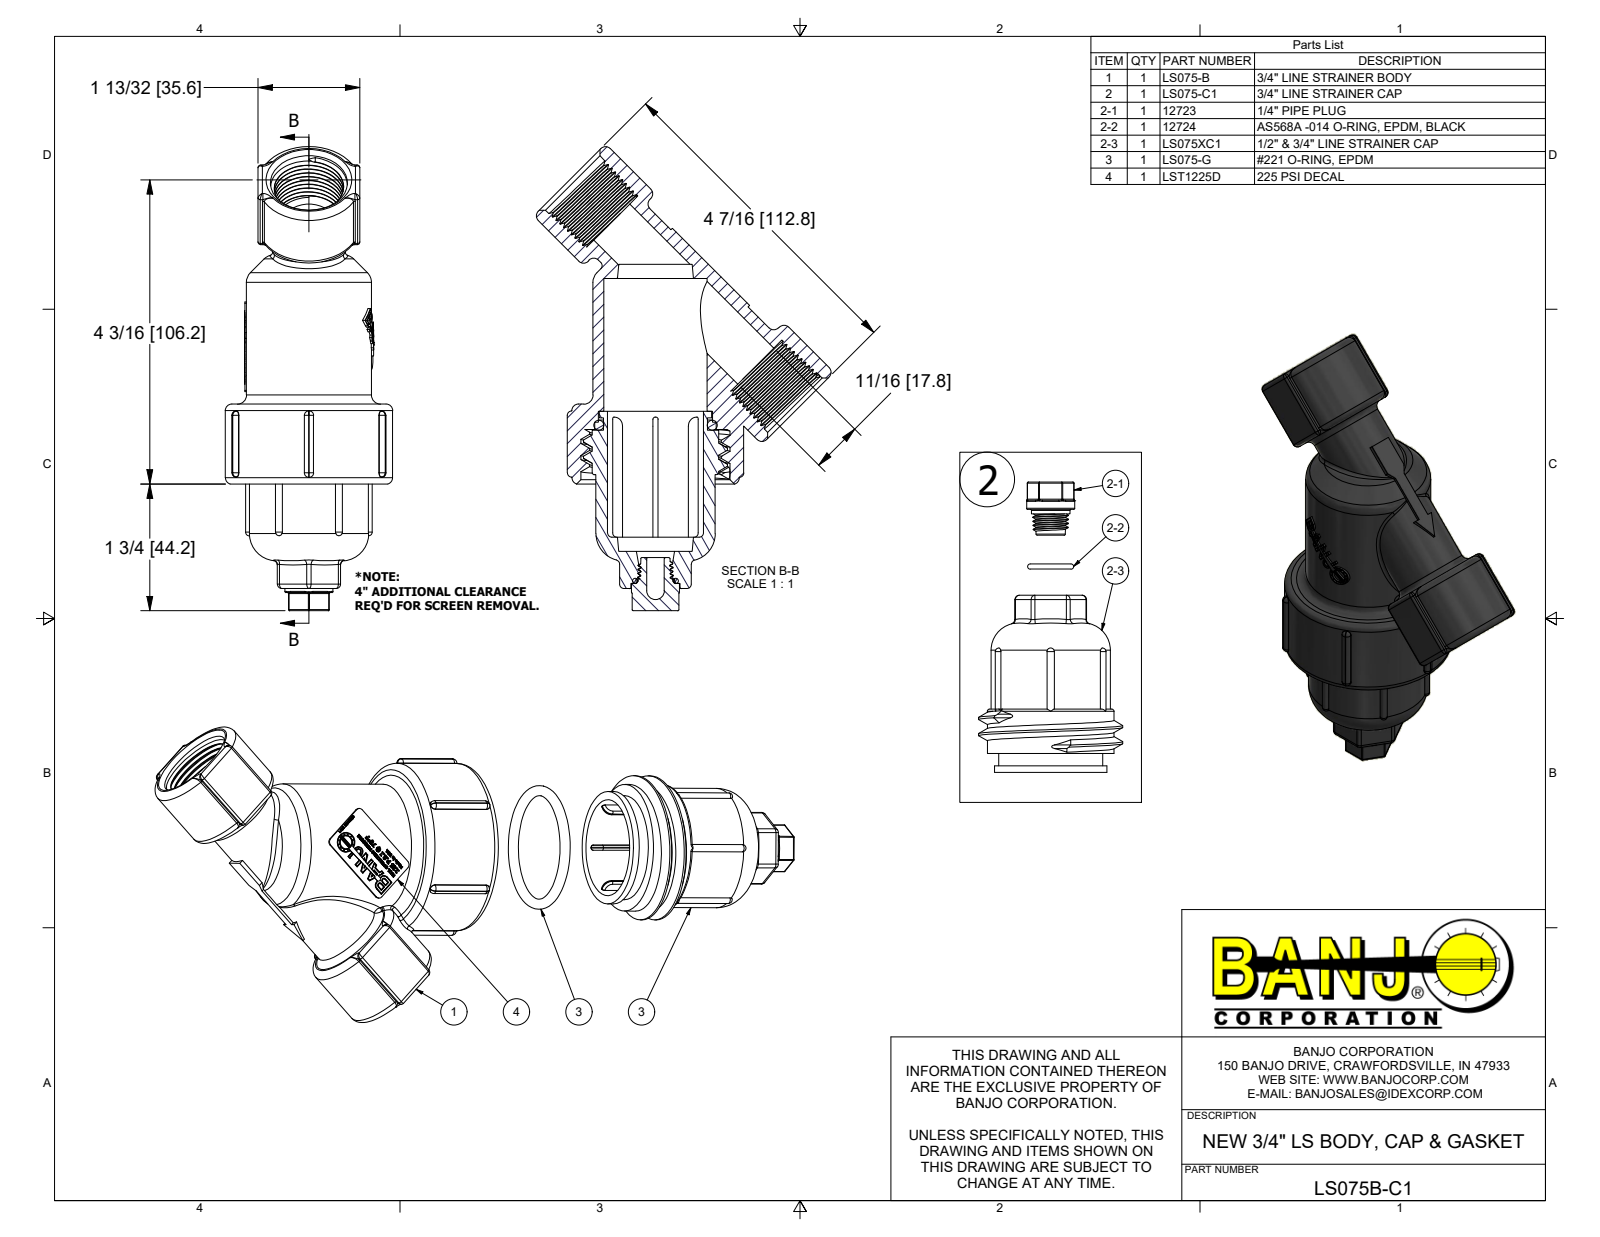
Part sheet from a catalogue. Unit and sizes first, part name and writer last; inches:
Units: inches
Overall size (bounding box): 21.064 × 21.064 × 2.3
Round holes (diameter × count): ⌀0.181 ×2, ⌀0.257 ×2, ⌀0.7 ×2, ⌀0.24 ×1, ⌀0.675 ×1, ⌀1.32 ×1, ⌀1.42 ×1, ⌀1.57 ×1, ⌀1.671 ×1, ⌀1.809 ×1, ⌀2.05 ×1
Round bosses / shafts (diameter × count): ⌀0.27 ×2, ⌀2.3 ×1, ⌀1.981 ×1, ⌀1.74 ×1, ⌀1.72 ×1, ⌀1.64 ×1, ⌀1.545 ×1, ⌀1.43 ×1
Partial cylindrical surfaces — rounded edges, fillets, slot ends (radius × count): R0.06 ×75, R0.03 ×34, R0.015 ×18, R0.125 ×8, R0.05 ×6, R0.026 ×4, R0.033 ×4, R0.063 ×4
Main face-to-face distances: 0.16, 0.25, 1.4, 1.56, 0.07, 1.58, 0.26, 0.02, 2.085, 2.075
Hole centre spacings: 0.638
Volume: 16.88 in³ · Surface area: 560.6 in²
Bodies: 7 solids, 1989 faces (1018 planar, 312 cylindrical, 659 other)
Part name (STEP PRODUCT): LS075B-C1; CE050D; LS075-B; LS075-C1 (+5 more)
STEP written by: Autodesk Inventor 2018 (AUTOMOTIVE_DESIGN)
